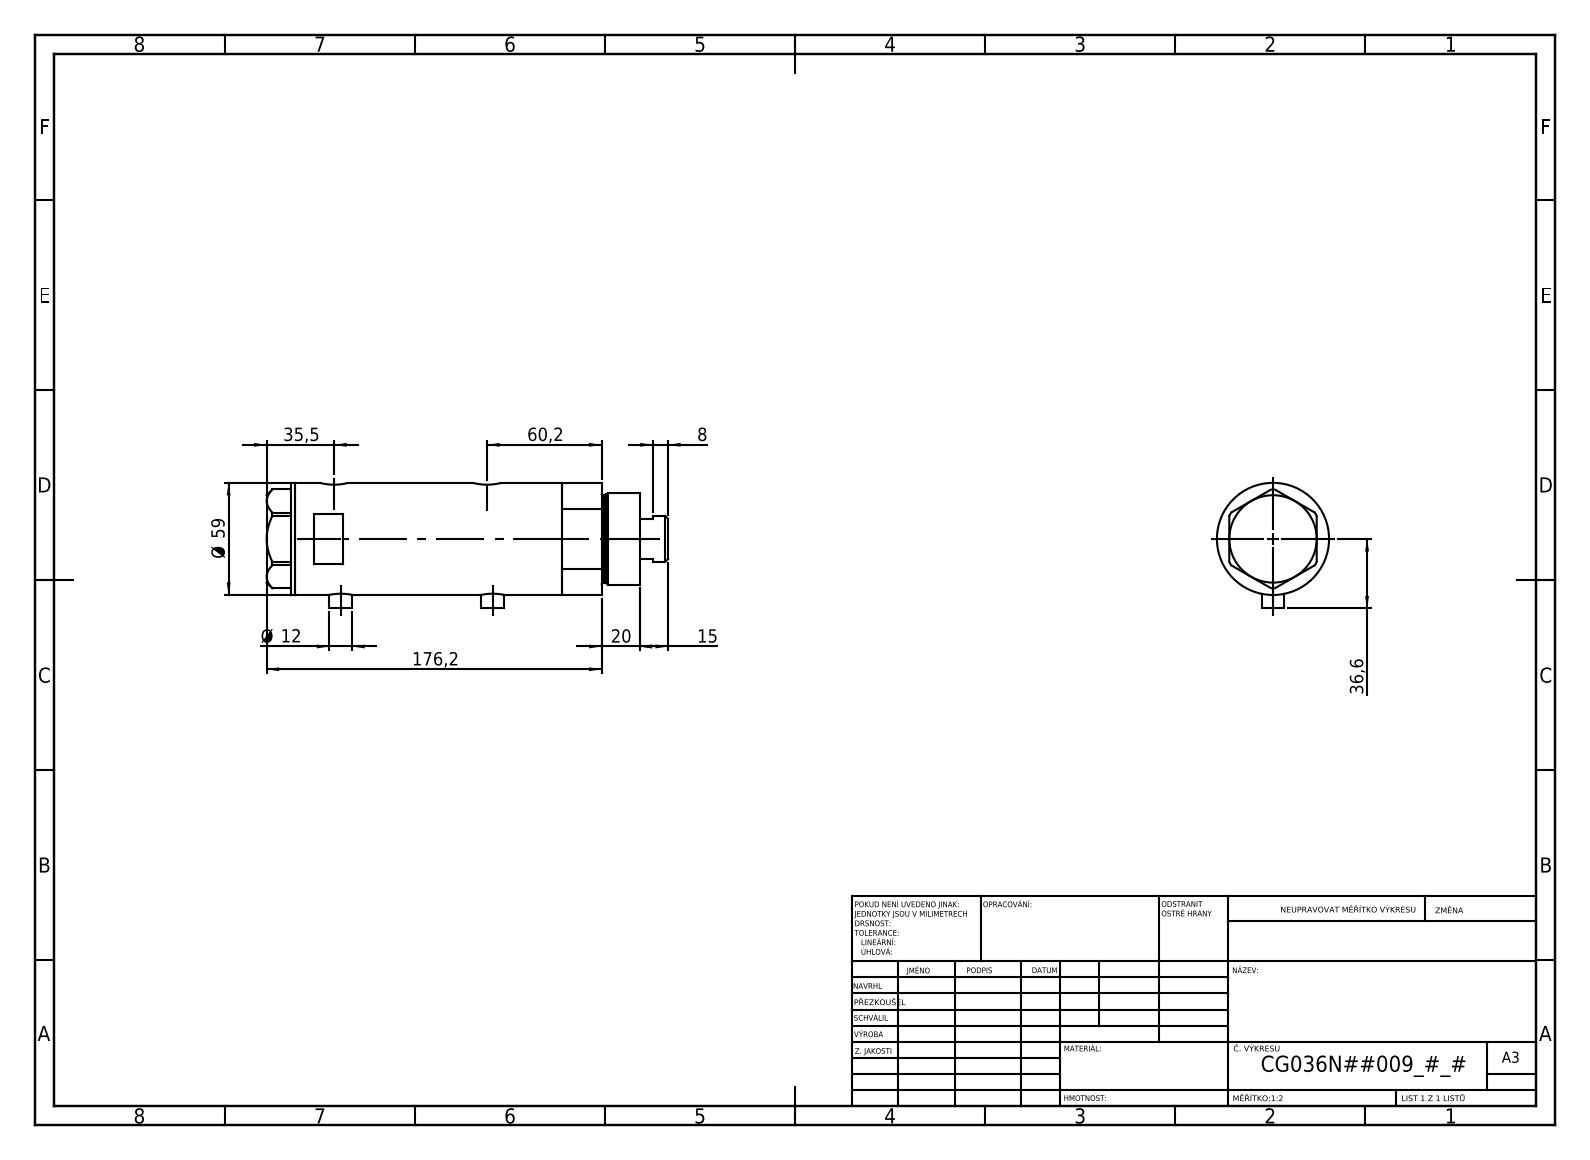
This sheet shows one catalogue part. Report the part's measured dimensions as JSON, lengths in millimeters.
{"part_name": "V270CG_BACK; V270CG_MIDDLE; V270CG_FRONT; V270CG_VC", "step_written_by": "SolidWorks 2019 (CONFIG_CONTROL_DESIGN)", "units": "millimeters", "bodies": {"solids": 4, "faces": 120, "planar": 51, "cylindrical": 49, "other": 20}, "overall_size": [211.2, 66.1, 59], "volume_mm3": 500051, "surface_area_mm2": 101392, "round_holes": [[9.73, 2], [12.5, 2], [15, 2], [8.5, 1], [25, 1], [26.5, 1], [36, 1], [40, 1], [52, 1]], "round_bosses_or_shafts": [[12, 2], [59, 1], [48, 1], [46, 1], [24, 1]], "face_to_face_distances": [102.2, 23.5, 78.7, 15, 38.5, 117.2, 2, 196.2, 181.2, 157.7], "hole_center_spacings": [2.9, 3.5, 77, 79.9, 80.5, 83.4]}
